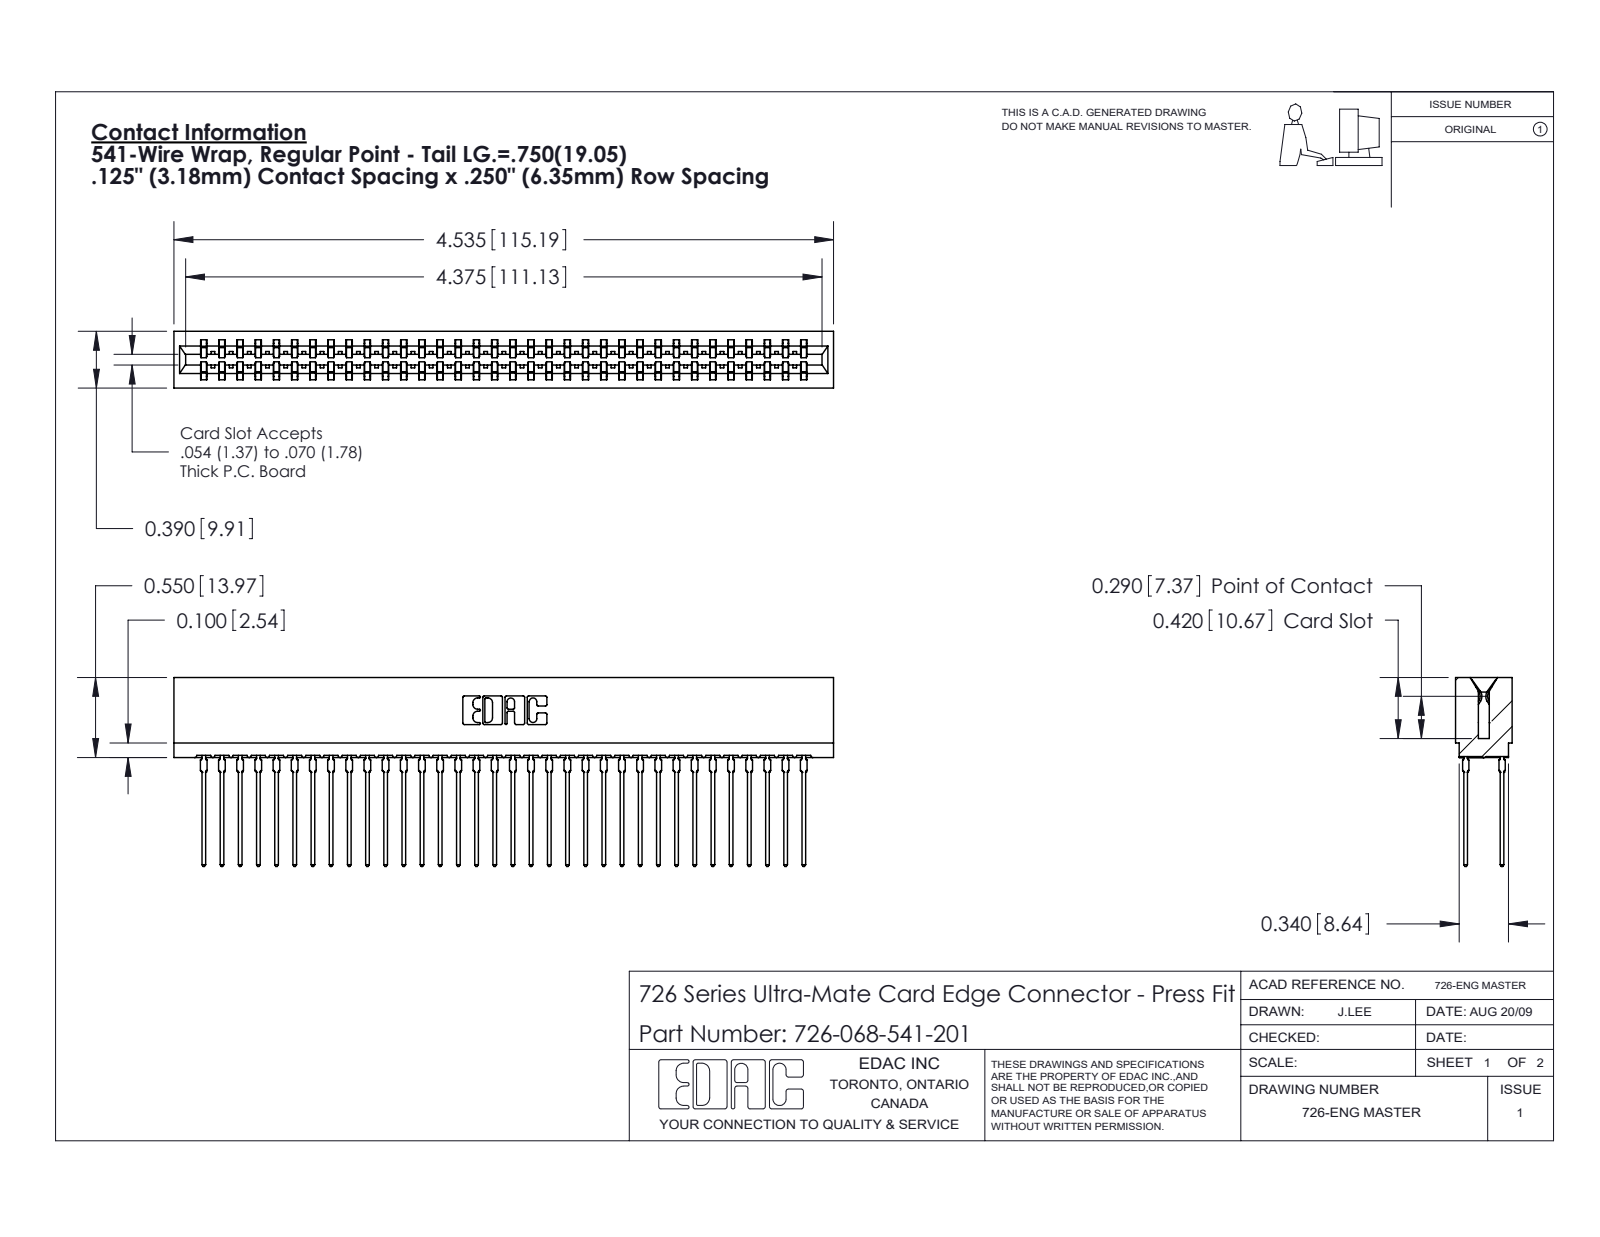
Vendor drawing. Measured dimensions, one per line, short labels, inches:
name: 726-068-541-201; 726 Part_.515 Slot Depth - 01; 746-292-001_541
written by: SolidWorks 2020 (CONFIG_CONTROL_DESIGN)
unit: in
bodies: 69 solids, 6183 faces (3183 planar, 1232 cylindrical, 1768 other)
size: 4.535 × 1.299 × 0.39
volume: 0.672 in³; area: 30.93 in²
rounds: 136× R0.021, 35× R0.015, 22× R0.01, 8× R0.005, 8× R0.011, 6× R0.007, 6× R0.031, 3× R0.026
face distances: 0.057, 0.333, 0.025, 0.307, 0.25, 0.083, 0.39, 0.275, 0.225, 0.365
